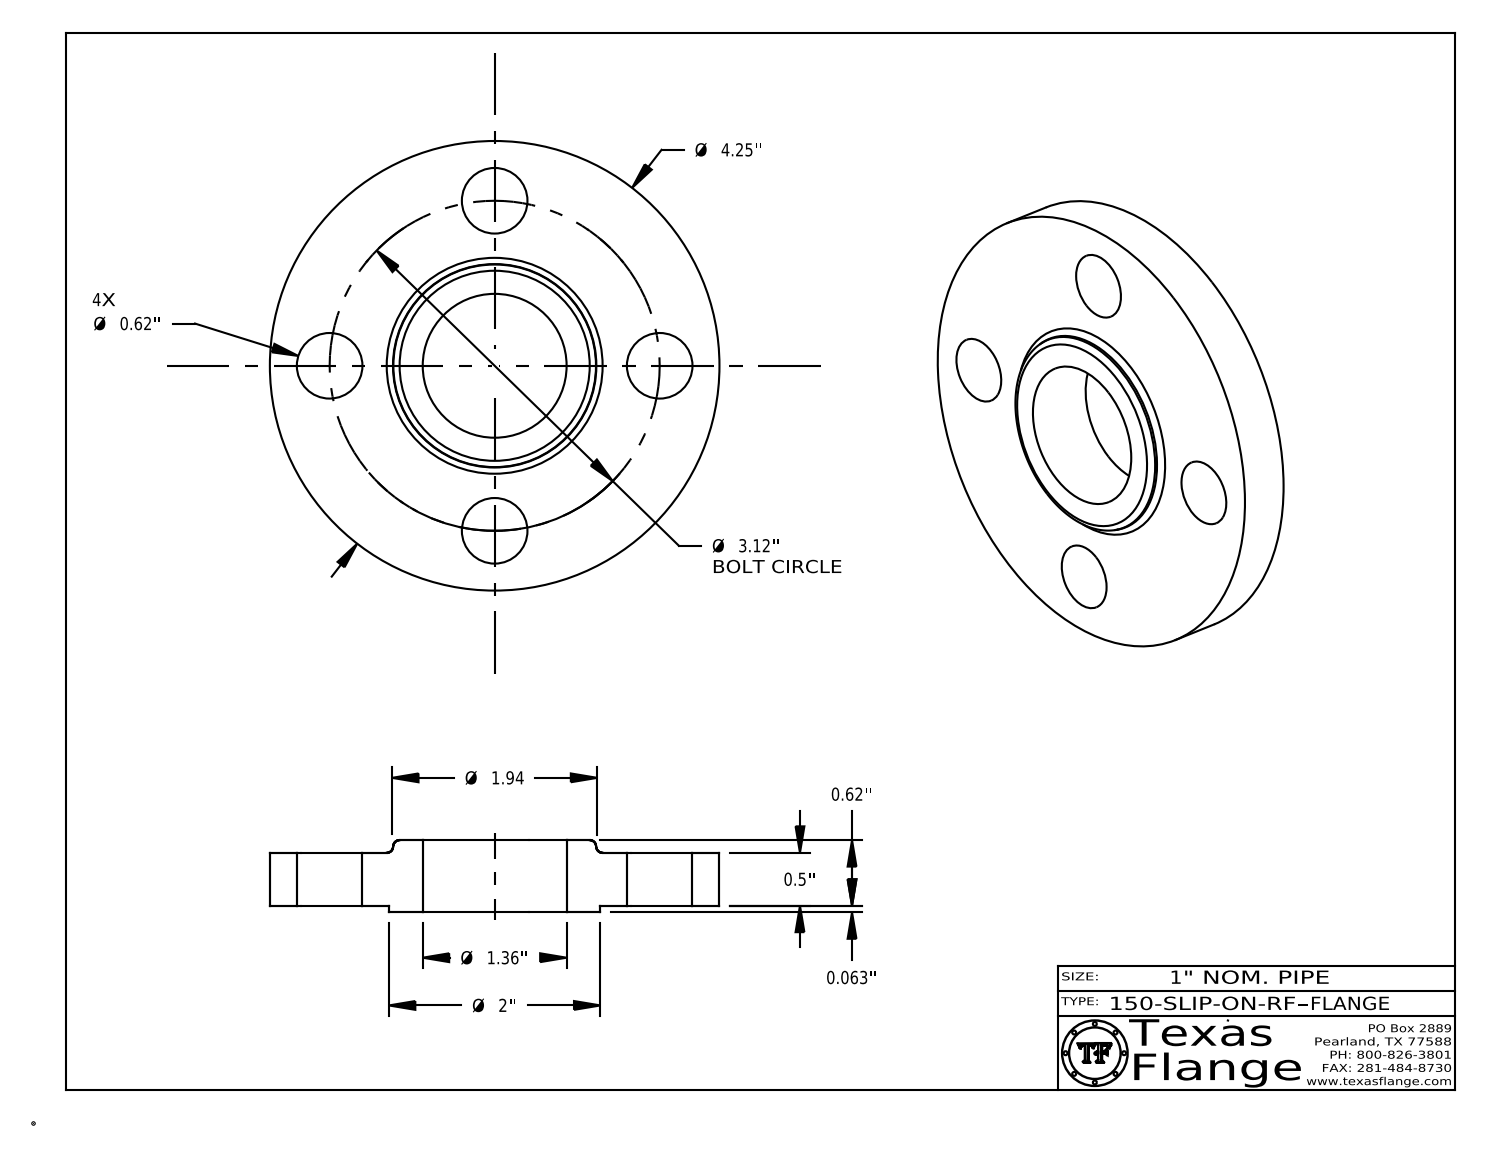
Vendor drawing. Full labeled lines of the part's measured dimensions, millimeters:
Part name (STEP PRODUCT): 150-SLIP-ON-RF
STEP written by: CATIA V5 STEP AP214 (AUTOMOTIVE_DESIGN)
Units: millimetres
Bodies: 1 solid, 409 faces (369 planar, 34 cylindrical, 6 other)
Overall size (bounding box): 108 × 108 × 17.3
Volume: 98 980 mm³ · Surface area: 24 150 mm²
Round holes (diameter × count): ⌀15.7 ×4, ⌀12.6 ×1, ⌀34.5 ×1
Round bosses / shafts (diameter × count): ⌀0.8 ×8, ⌀108 ×1, ⌀50.8 ×1, ⌀9.9 ×1
Main face-to-face distances: 12.7, 1.6, 14.3, 17.3, 15.7, 3, 13.9, 12.3, 0.4, 3.4
Hole centre spacings: 39.6, 56, 30.3, 73.2, 79.2, 39.6
